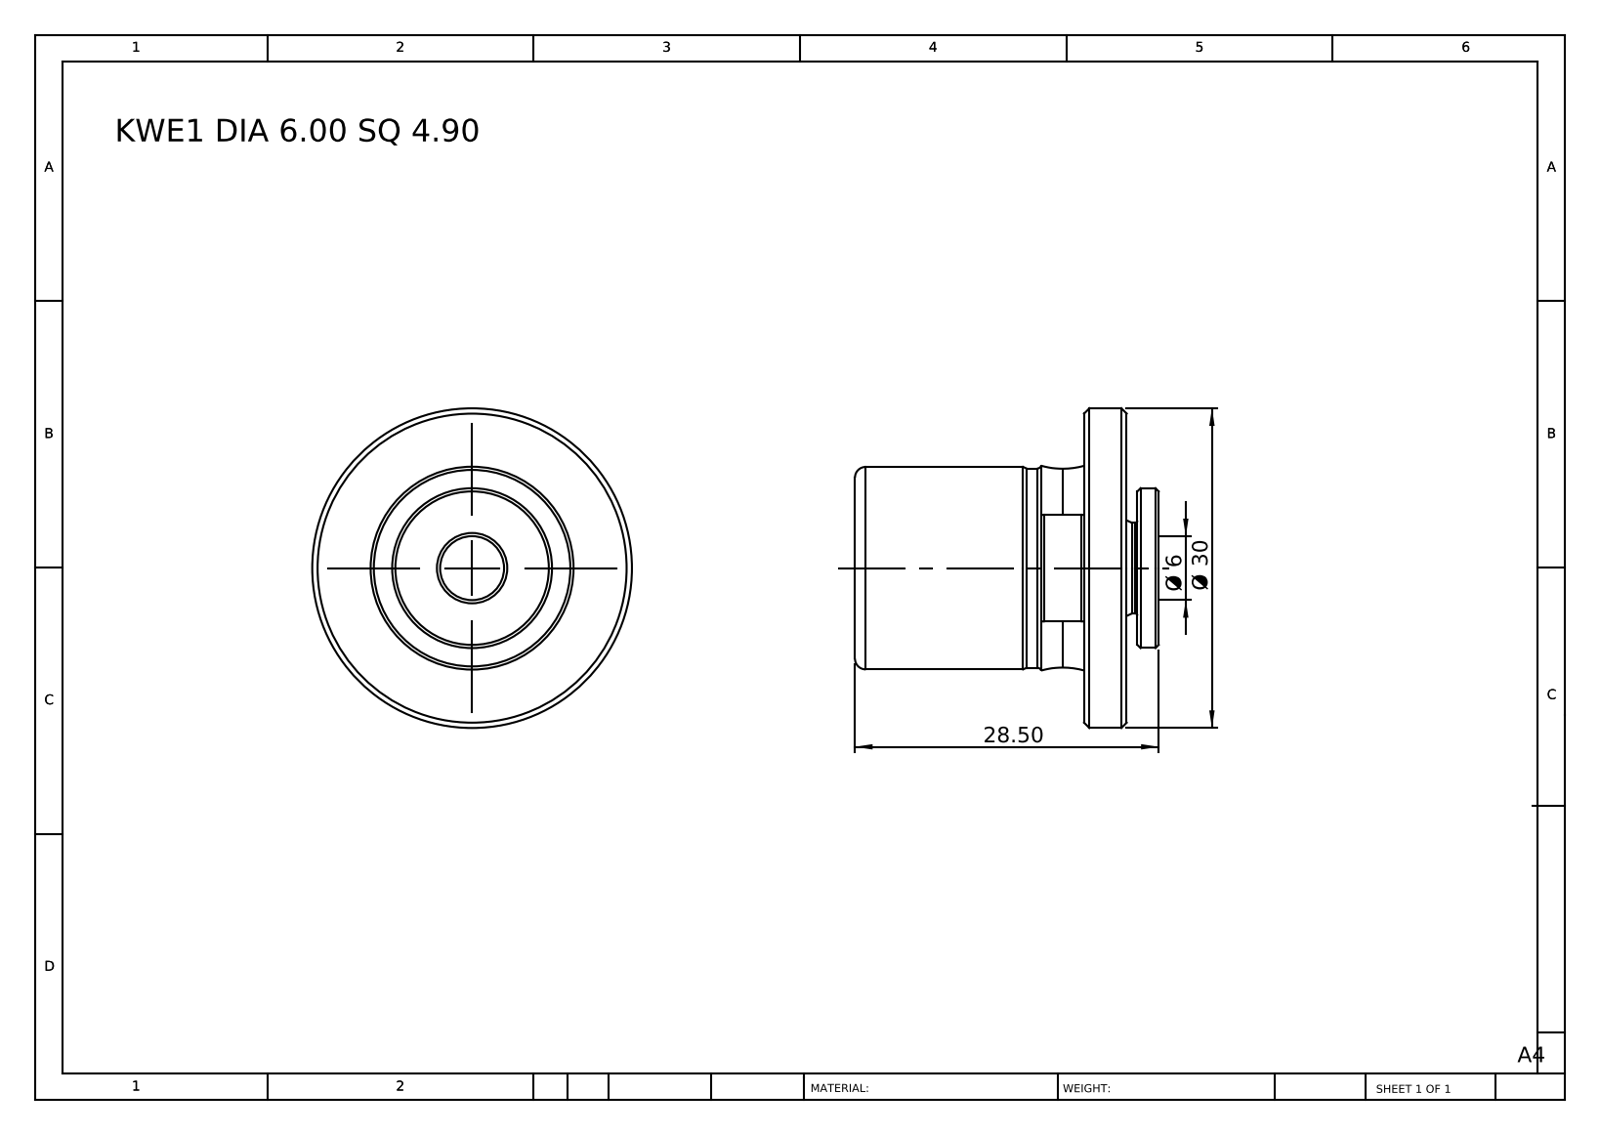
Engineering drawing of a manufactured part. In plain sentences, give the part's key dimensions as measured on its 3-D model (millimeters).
The part is named "KWE1 DIA 6.00 SQ 4.90". Its 3-D file was written by "SolidWorks 2014 (CONFIG_CONTROL_DESIGN)". It is 1 solid with 61 faces: 13 planar, 16 cylindrical and 32 other. Overall it measures 30 by 30 by 28.5 millimeters. Its volume is 9 083 cubic millimeters and its surface area 3 691 square millimeters. Round holes: 1 of diameter 6, 1 of diameter 19.04. Round bosses or shafts: 1 of diameter 30, 1 of diameter 19, 1 of diameter 18.7, 1 of diameter 15, 1 of diameter 8.5. Partial cylindrical surfaces (rounded edges, fillets, slot ends): 1 of radius 12.4. The main face-to-face distances are 4, 21.5, 25.5, 28.5, 7, 3, 26.5, 5, 1, 2.
